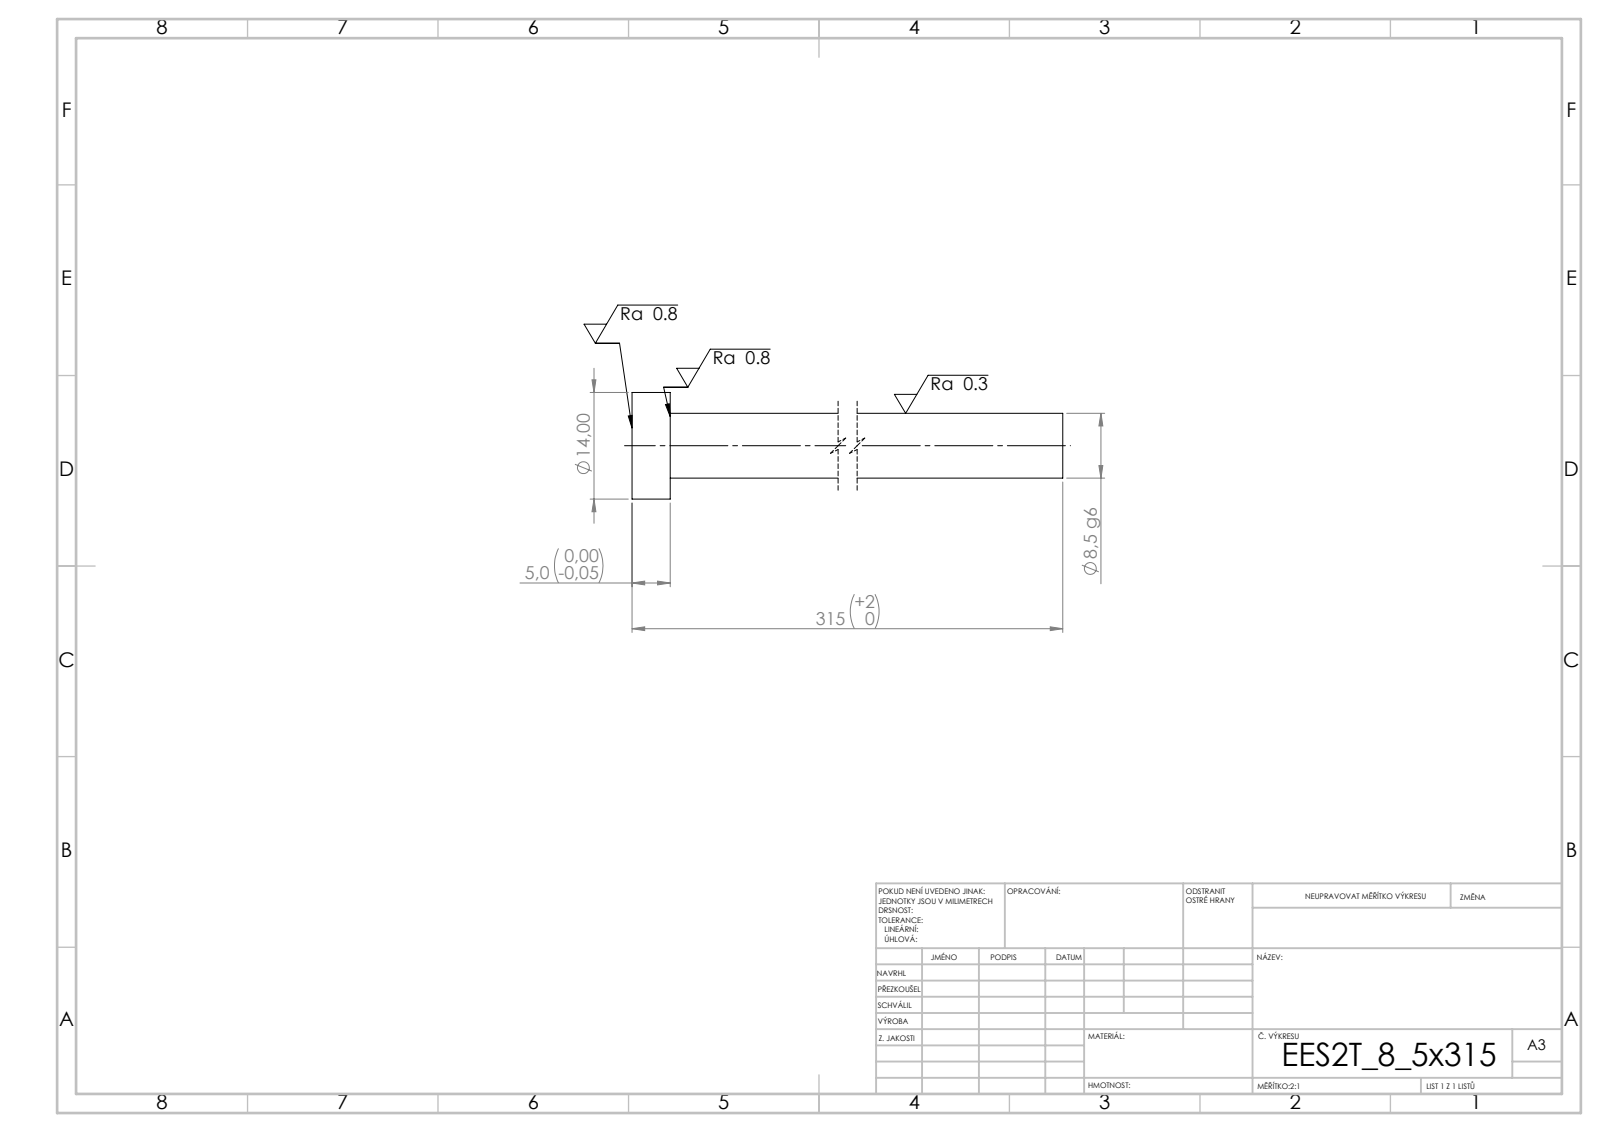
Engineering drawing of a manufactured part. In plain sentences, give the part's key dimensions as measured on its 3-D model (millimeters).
Its 3-D file was written by "SolidWorks 2019 (CONFIG_CONTROL_DESIGN)". It is 1 solid with 7 faces: 3 planar, 4 cylindrical and 0 other. Overall it measures 315 by 14 by 14 millimeters. Its volume is 18 361 cubic millimeters and its surface area 8 806 square millimeters. Round bosses or shafts: 1 of diameter 14, 1 of diameter 8.5. The main face-to-face distances are 5, 315, 310.
